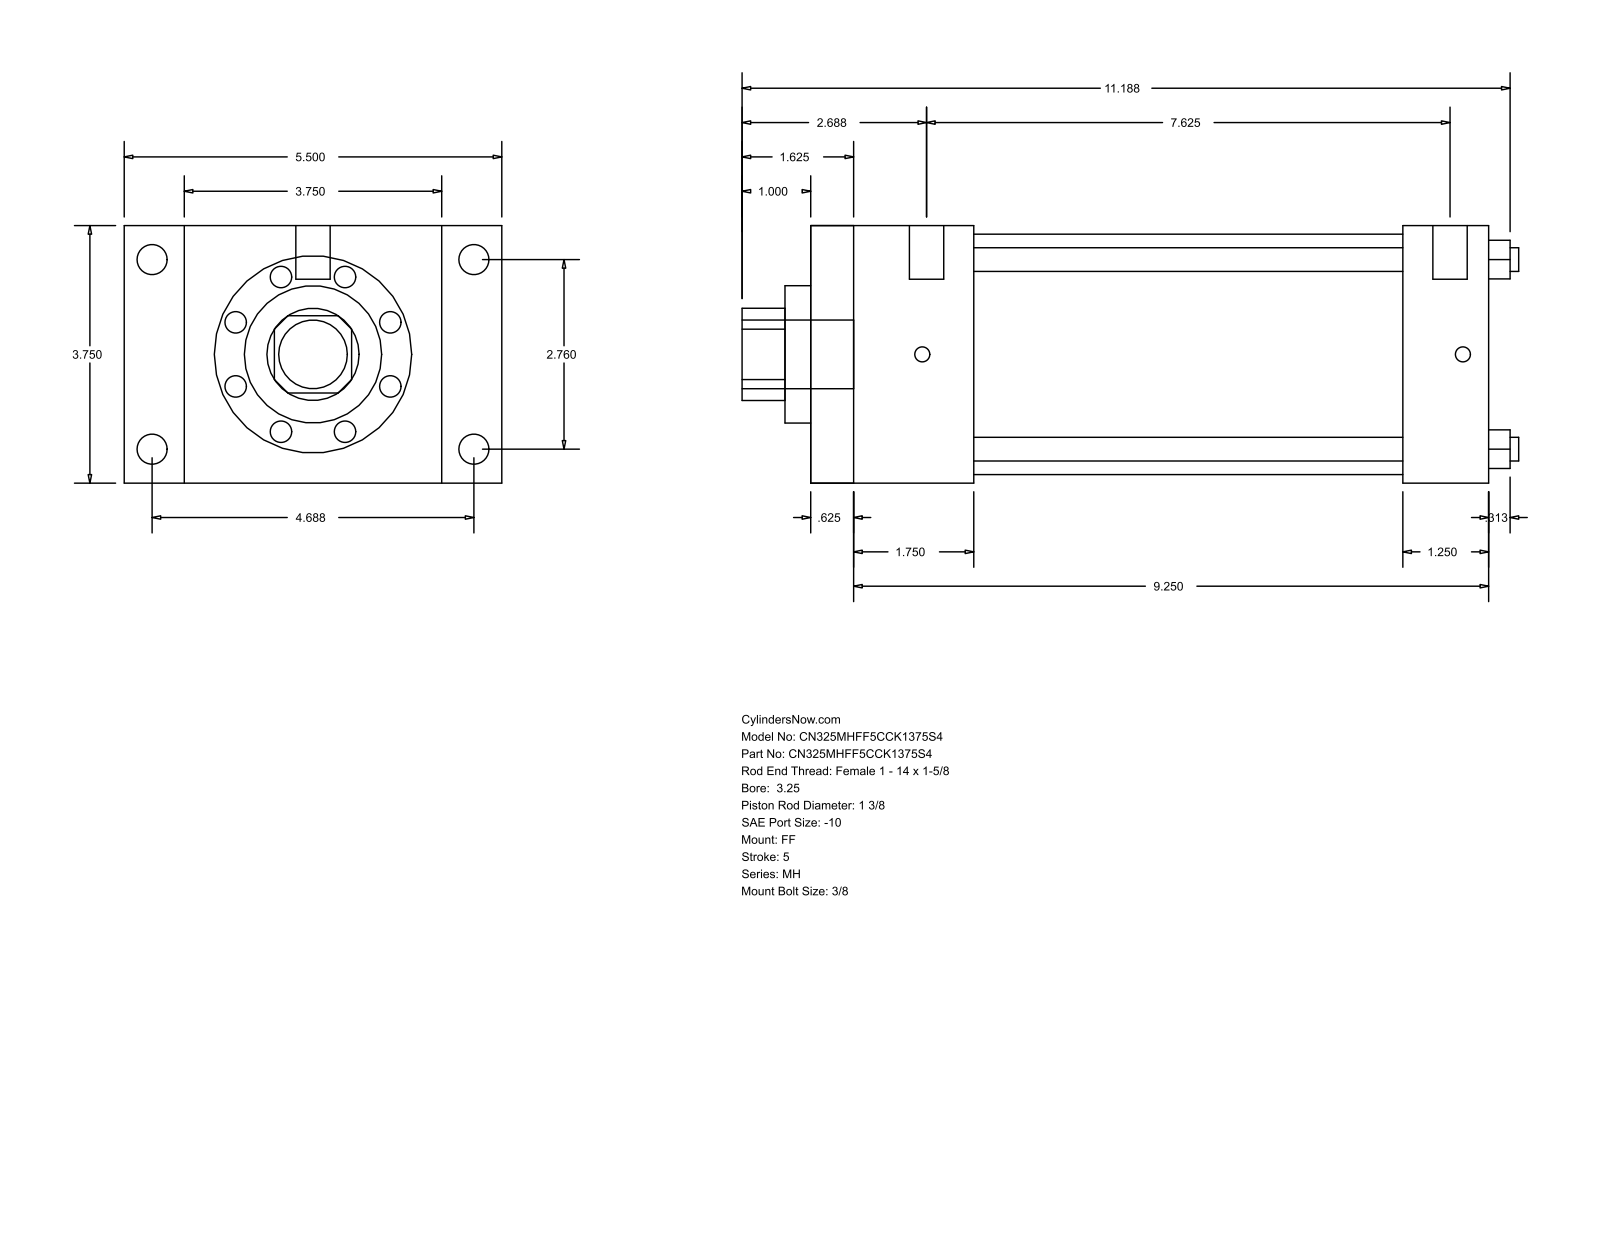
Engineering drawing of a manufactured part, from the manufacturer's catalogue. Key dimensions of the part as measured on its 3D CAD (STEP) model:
Part name (STEP PRODUCT): MH_FF__0325_1.375
STEP written by: GSSL Pune (CONFIG_CONTROL_DESIGN)
Units: millimetres
Bodies: 0 solids, 92 faces (64 planar, 28 cylindrical, 0 other)
Overall size (bounding box): 287.34 × 139.7 × 95.25
Round holes (diameter × count): ⌀8.76 ×4, ⌀34.92 ×1, ⌀50.8 ×1, ⌀88.9 ×1
Round bosses / shafts (diameter × count): ⌀11.13 ×4, ⌀5.56 ×4, ⌀12.7 ×2, ⌀25.4 ×1
Partial cylindrical surfaces — rounded edges, fillets, slot ends (radius × count): R17.06 ×1
Main face-to-face distances: 95.24, 250.83, 15.87, 234.96, 22.23, 117.47, 219.07, 203.2, 31.76, 60.32
Hole centre spacings: 49.57, 70.1, 99.14
